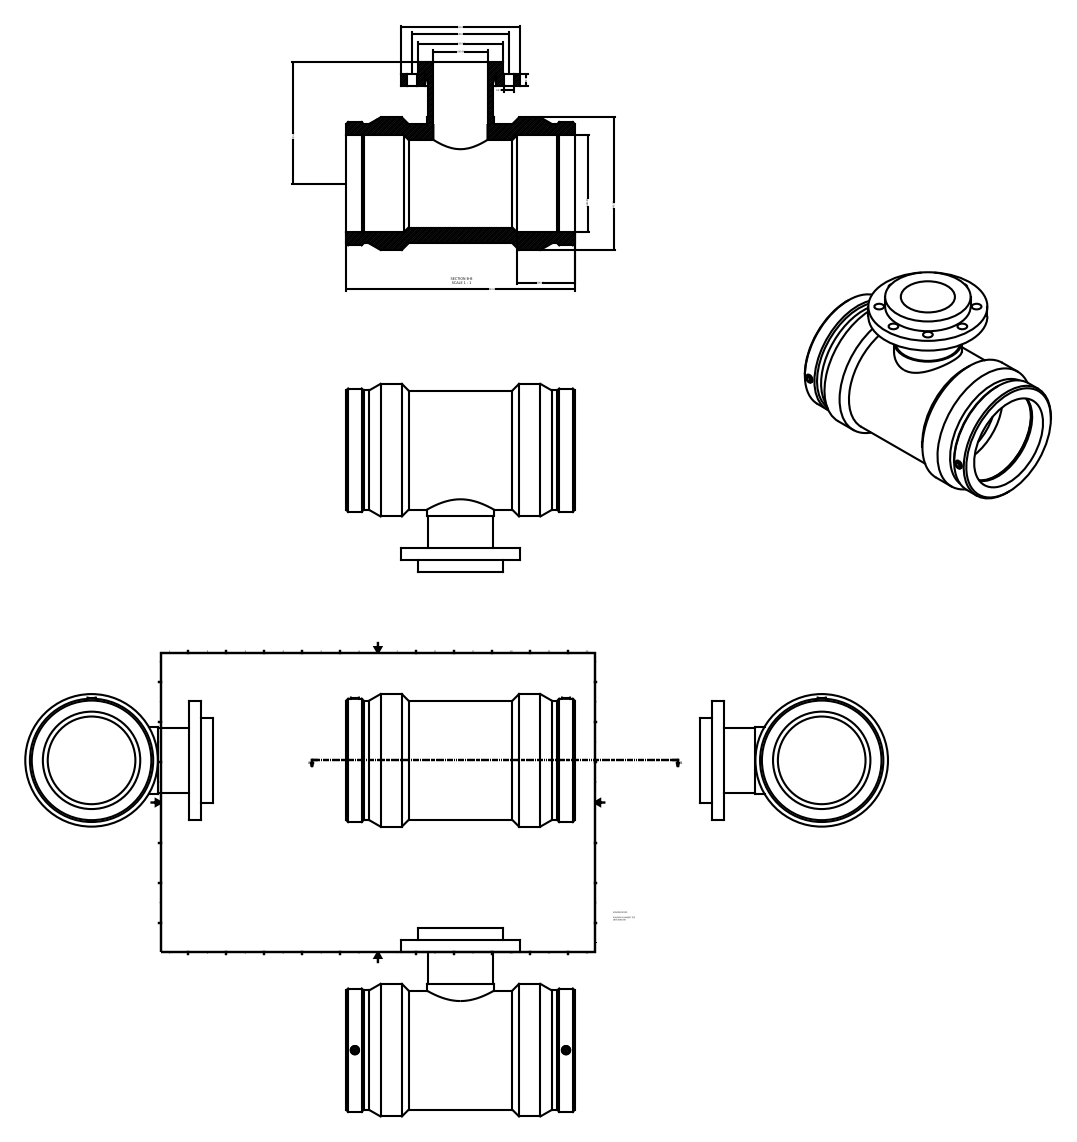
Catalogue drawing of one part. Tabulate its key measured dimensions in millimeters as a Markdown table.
| quantity | value |
| --- | --- |
| part name | 499404180100 |
| STEP written by | Autodesk Inventor 2015 (AUTOMOTIVE_DESIGN) |
| units | millimeters |
| bodies | 1 solid, 60 faces (14 planar, 30 cylindrical, 16 other) |
| overall size | 422 × 347.5 × 245 |
| volume | 8 404 000 mm³ |
| surface area | 740 876 mm² |
| round holes (diameter × count) | 18 × 8, 10 × 2, 100 × 1, 130 × 1, 162 × 1, 180 × 1 |
| round bosses / shafts (diameter × count) | 4 × 2, 245 × 1, 227.85 × 1, 221.01 × 1, 220.5 × 1, 220 × 1, 158 × 1, 125 × 1 |
| main face-to-face distances | 22, 422, 44, 102.5, 80.5, 58.5, 31.91, 390.09, 358.18, 14 |
| hole center spacings | 68.88, 90, 127.28, 166.3, 180, 390.2 |
